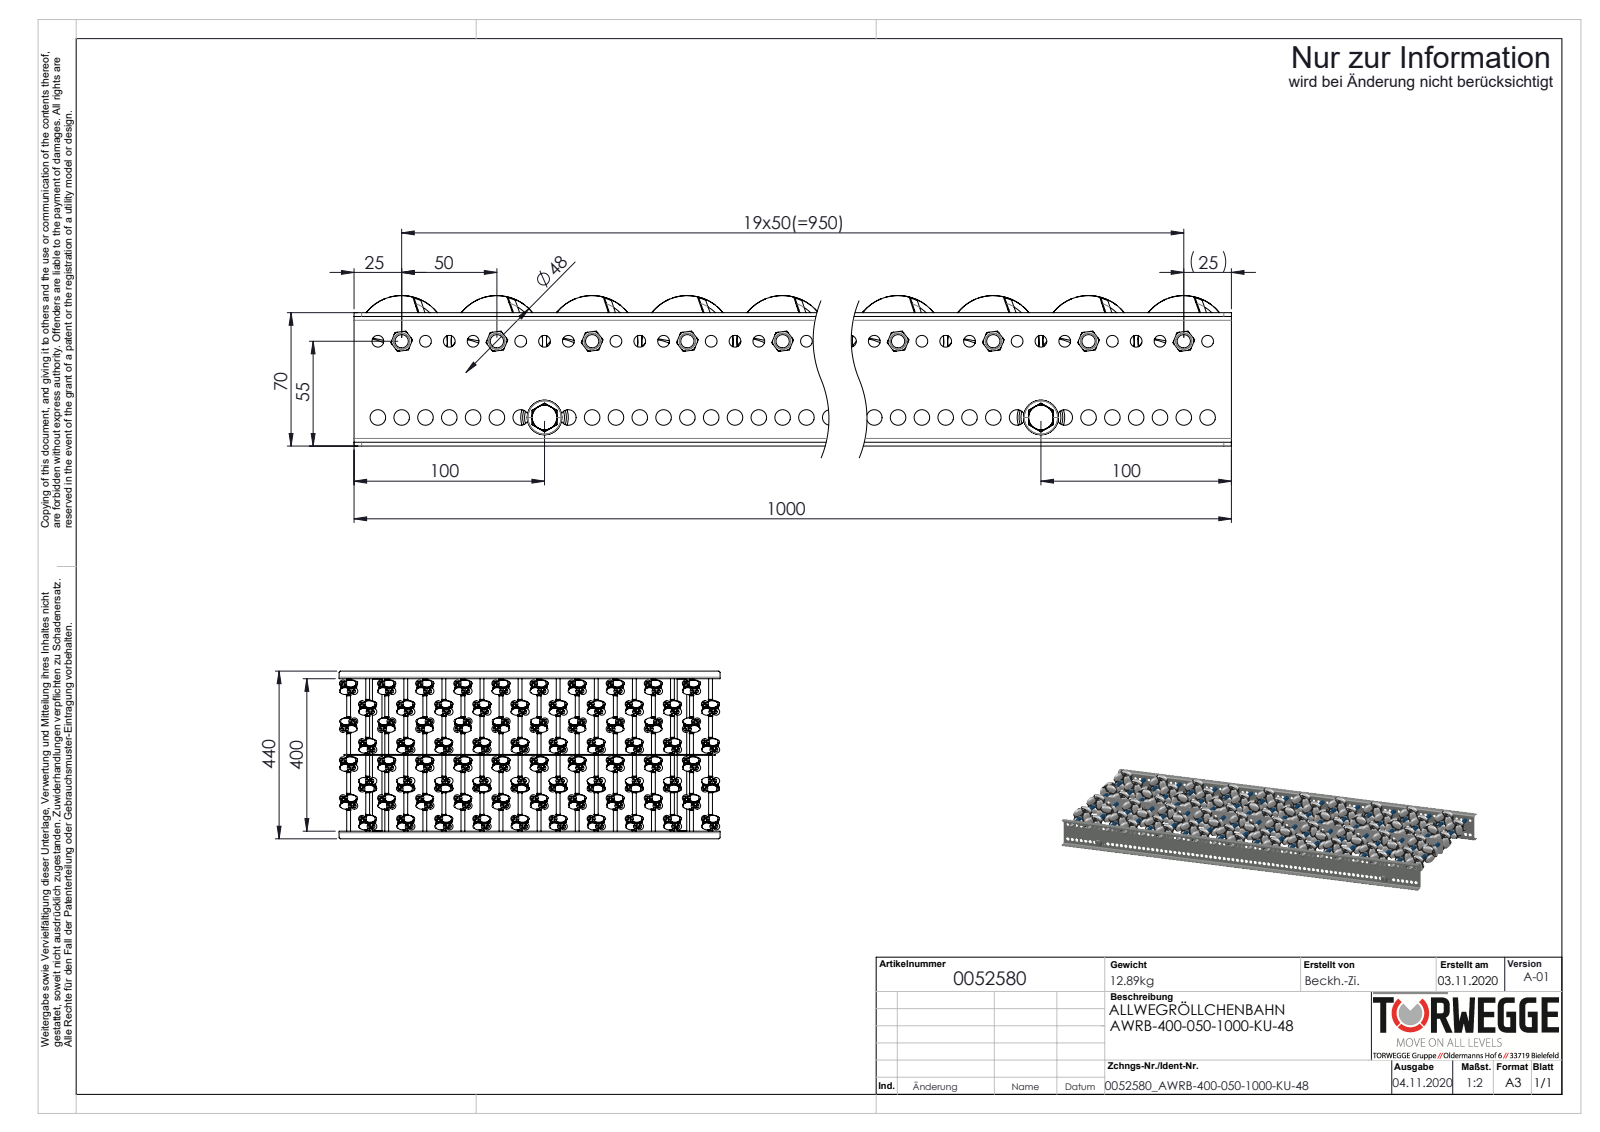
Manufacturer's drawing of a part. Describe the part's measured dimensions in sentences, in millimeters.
The part is named "0052580; 0027528_BUCHSE-HOHLNIETE ZU AWR48; Traversen_KFG_L400; AWR48_Röllchen (+8 more)". Its 3-D file was written by "SolidWorks 2020 (AUTOMOTIVE_DESIGN)". It is 1353 solids with 24080 faces: 8326 planar, 9290 cylindrical and 6464 other. Overall it measures 1000 by 440 by 78.99 millimeters. Its volume is 4 480 000 cubic millimeters and its surface area 3 051 000 square millimeters. Round holes: 480 of diameter 3.7, 480 of diameter 4.2, 79 of diameter 6.2, 79 of diameter 8.2, 39 of diameter 6.5, 20 of diameter 4.92, 20 of diameter 8.4, 2 of diameter 6.8, 2 of diameter 21. Round bosses or shafts: 480 of diameter 4, 421 of diameter 3.7, 22 of diameter 8, 20 of diameter 42, 20 of diameter 11, 20 of diameter 10, 20 of diameter 7, 20 of diameter 6. Partial cylindrical surfaces (rounded edges, fillets, slot ends): 20 of radius 23.55, 8 of radius 4, 4 of radius 2, 4 of radius 5. The main face-to-face distances are 2, 402, 68, 400, 404, 200.6, 198.6, 201.4, 203.4, 203.1. The hole center spacings are 36.06, 36.05, 100, 50, 36.07, 36.04, 200, 30.99.
